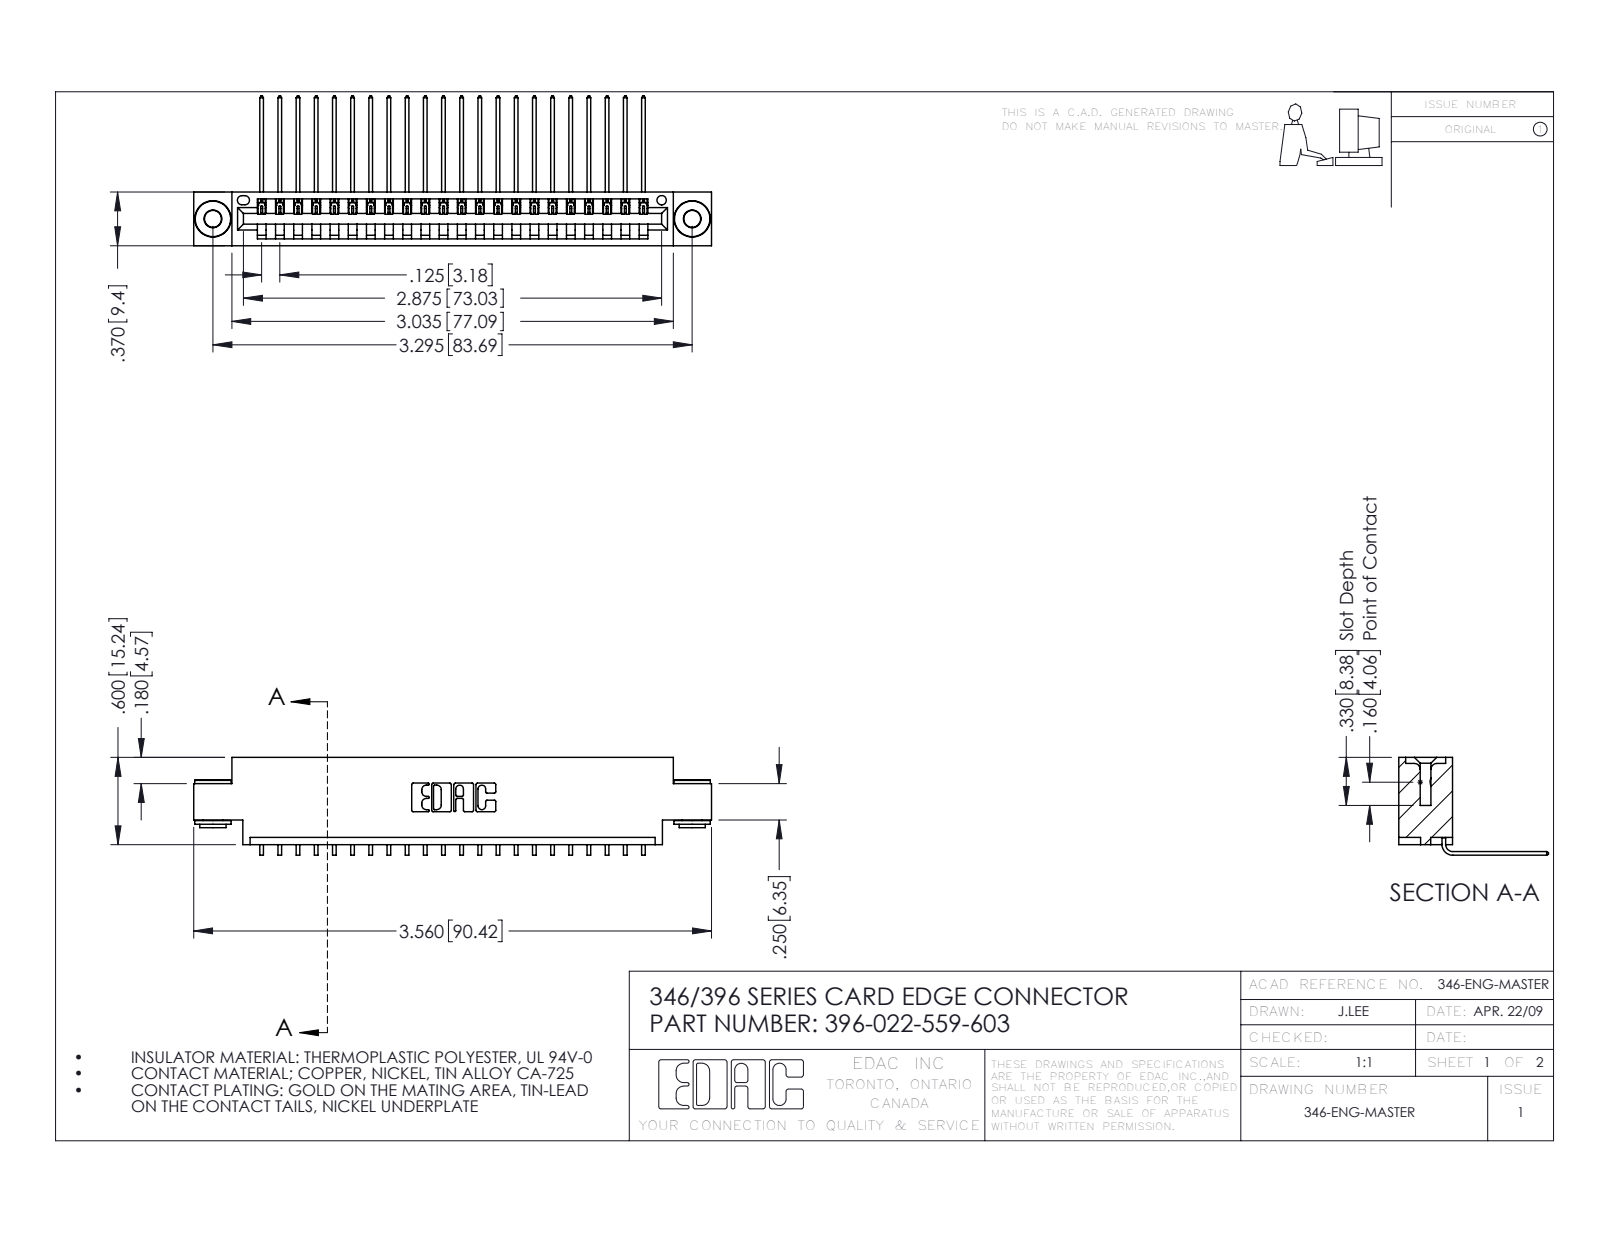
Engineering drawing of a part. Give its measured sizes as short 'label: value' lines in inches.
name: 346 Part_0.170 Offset - 0.156 Dia-TH; 345-292-001_558 559 Tail - 1; 396-022-559-603; 345-250-002_345-250-002-102
written by: SolidWorks 2016 (CONFIG_CONTROL_DESIGN)
unit: in
bodies: 25 solids, 1484 faces (1014 planar, 462 cylindrical, 8 other)
size: 3.56 × 1.03 × 0.673
volume: 0.516 in³; area: 17.31 in²
holes: 2× ⌀0.116, 2× ⌀0.156, 1× ⌀0.064
bosses: 2× ⌀0.25, 2× ⌀0.18, 2× ⌀0.136
rounds: 44× R0.006, 22× R0.01, 6× R0.007, 6× R0.031, 3× R0.026, 2× R0.031, 2× R0.04, 1× R0.014
face distances: 0.048, 0.37, 0.322, 0.25, 0.025, 0.072, 0.148, 0.222, 0.1, 0.174
hole spacings: 0.246, 3.087, 3.295
